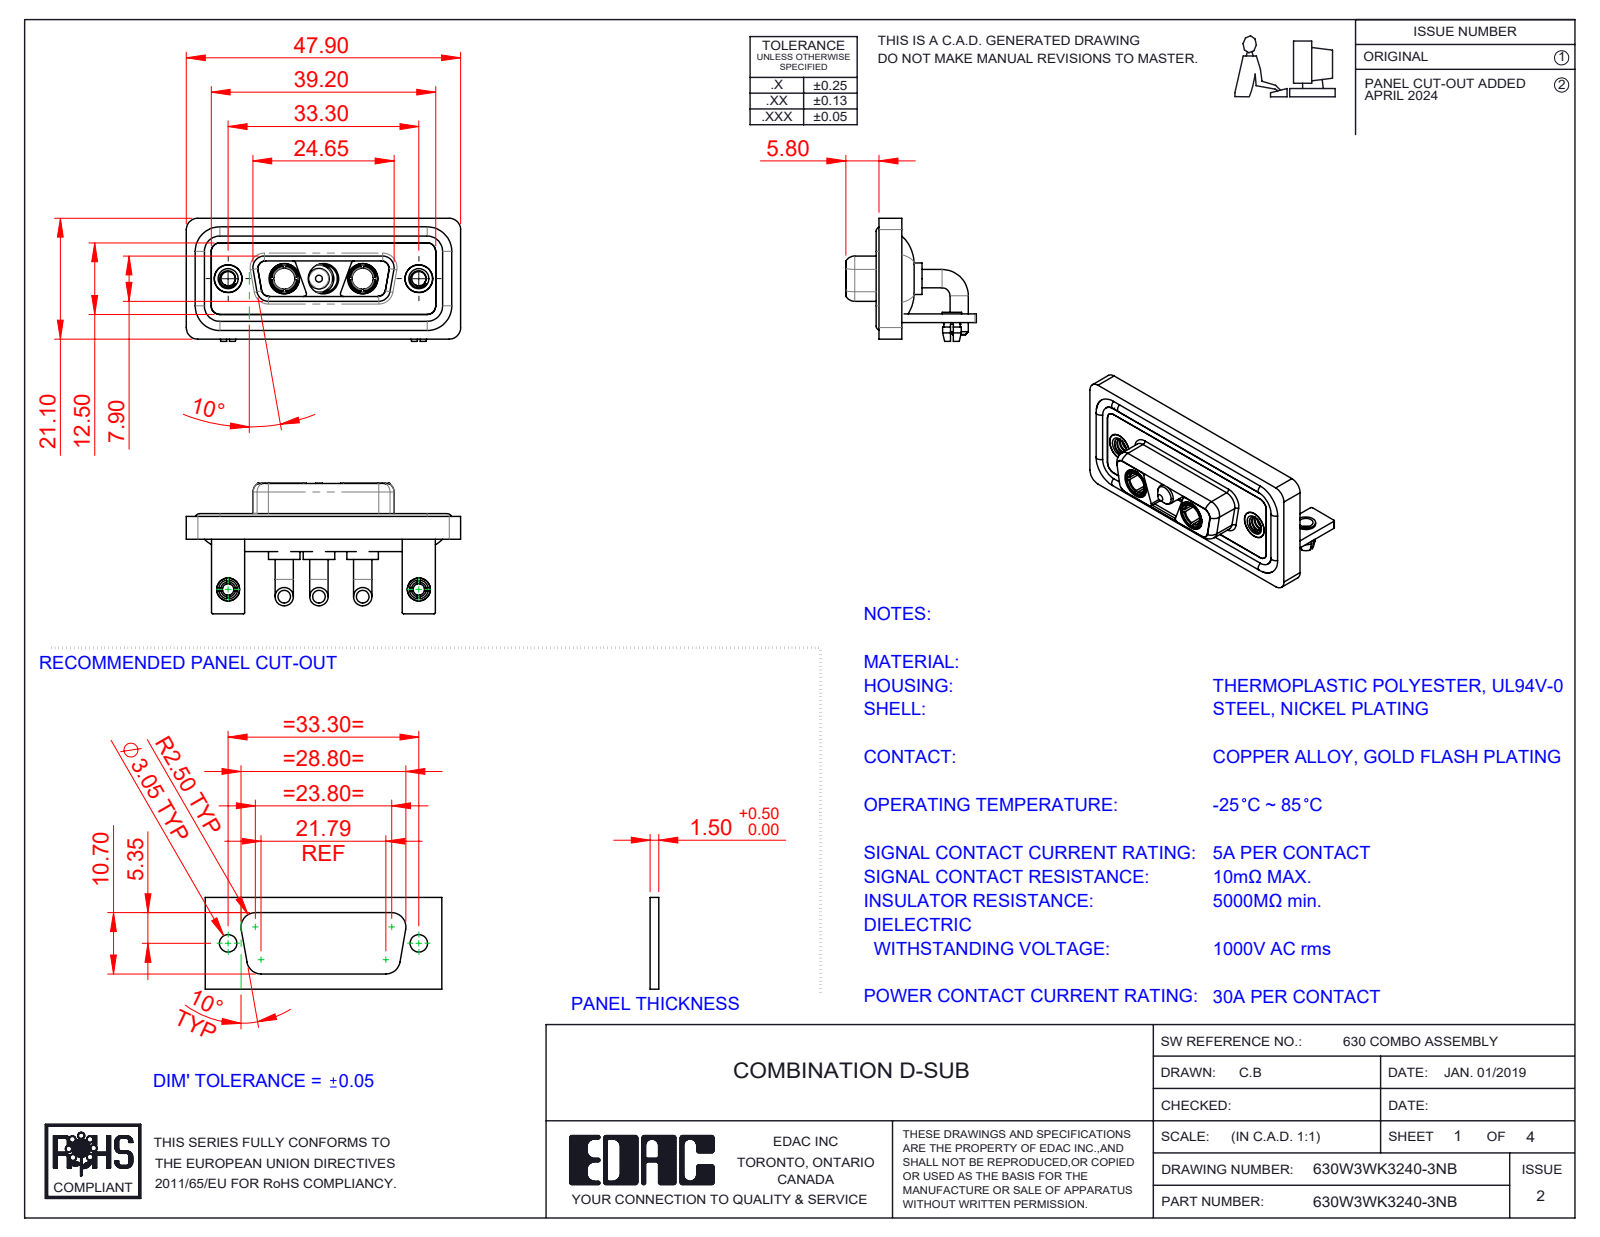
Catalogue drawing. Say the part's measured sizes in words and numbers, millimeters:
The part is named "630W3WK3240-3NB; Power Socket_30A RA; Power Pin_30A RA; 630Combo Board Lock_50 Contacts (+6 more)". Its 3-D file was written by "SolidWorks 2023 (CONFIG_CONTROL_DESIGN)". It is 17 solids with 729 faces: 246 planar, 318 cylindrical and 165 other. Overall it measures 47.9 by 22.8 by 21.5 millimeters. Its volume is 6 512 cubic millimeters and its surface area 10 743 square millimeters. Round holes: 5 of diameter 4.85, 4 of diameter 2.5, 3 of diameter 5.3, 2 of diameter 2, 2 of diameter 3.2, 2 of diameter 3.7, 2 of diameter 4, 2 of diameter 4.05, 2 of diameter 5. Round bosses or shafts: 6 of diameter 3.2, 4 of diameter 1.6, 3 of diameter 5.5, 3 of diameter 5.2, 3 of diameter 4.75, 3 of diameter 3.75, 2 of diameter 4.96, 2 of diameter 4.95. Partial cylindrical surfaces (rounded edges, fillets, slot ends): 21 of radius 2, 18 of radius 1.5, 16 of radius 0.25, 12 of radius 1.35, 9 of radius 0.5, 8 of radius 1.6, 4 of radius 0.6, 4 of radius 0.65. The main face-to-face distances are 0.4, 2.9, 1.5, 3.7, 1.8, 1.1, 4.1, 1.6, 2.5, 1.4. The hole center spacings are 6.85, 9.8, 16.65, 23.5, 33.3, 13.7.
